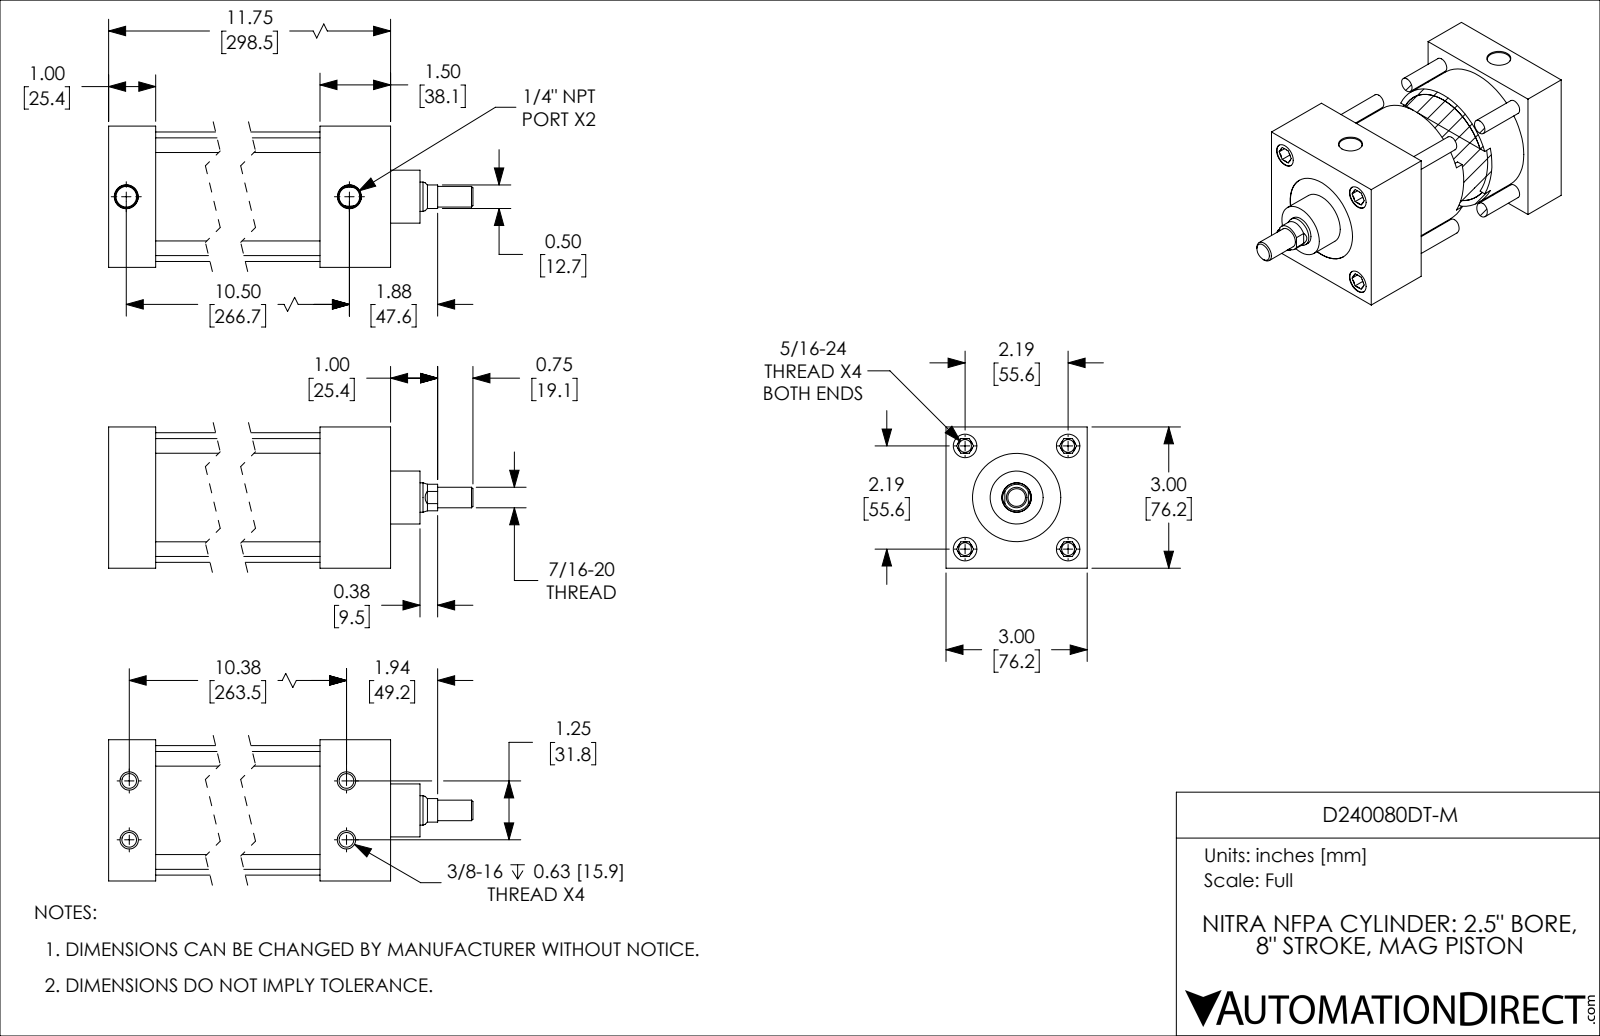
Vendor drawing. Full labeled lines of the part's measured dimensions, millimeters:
Part name (STEP PRODUCT): D240080DT-M_PISTON_KK1; D240080DT-M; D240080DT-M_BODY
STEP written by: SolidWorks 2019 (CONFIG_CONTROL_DESIGN)
Units: millimetres
Bodies: 2 solids, 200 faces (58 planar, 62 cylindrical, 80 other)
Overall size (bounding box): 342.9 × 76.2 × 76.2
Volume: 707 600 mm³ · Surface area: 200 800 mm²
Round holes (diameter × count): ⌀6.9 ×4, ⌀8 ×4, ⌀12.7 ×4, ⌀11.1 ×2, ⌀15.9 ×1, ⌀47.6 ×1, ⌀63.5 ×1
Round bosses / shafts (diameter × count): ⌀7.9 ×4, ⌀69.9 ×1, ⌀63.5 ×1, ⌀28.6 ×1, ⌀15.8 ×1, ⌀11.1 ×1
Partial cylindrical surfaces — rounded edges, fillets, slot ends (radius × count): R7.1 ×1
Main face-to-face distances: 76.2, 25.4, 260.4, 235, 298.5, 273.1, 38.1, 31.8, 57.2, 203.2
Hole centre spacings: 39.3, 55.6, 16, 16, 31.8, 78.7, 263.5, 265.4
